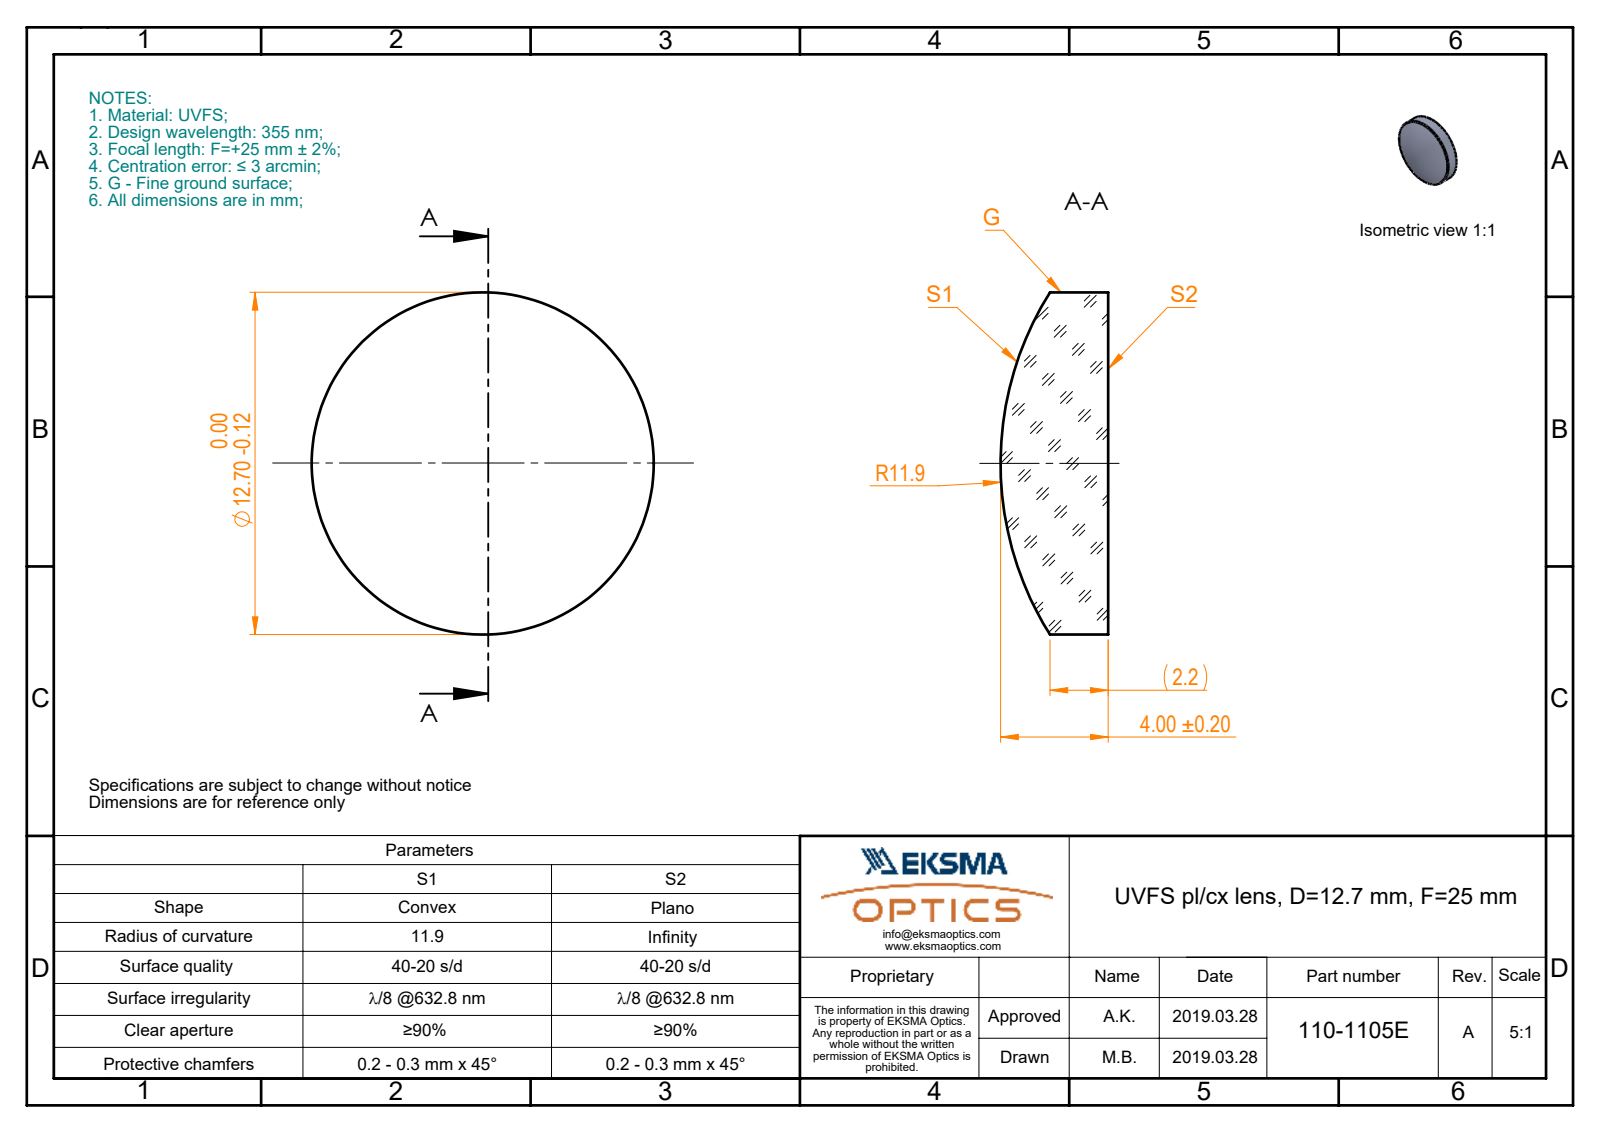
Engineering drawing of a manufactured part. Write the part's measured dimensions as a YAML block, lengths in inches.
part_name: "110-1105E UVFS pl-cx 12.7 F25"
step_written_by: "SolidWorks 2017 (CONFIG_CONTROL_DESIGN)"
units: inches
bodies: {solids: 1, faces: 5, planar: 1, cylindrical: 2, other: 2}
overall_size: [0.5, 0.5, 0.157]
volume: 0.024
surface_area: 0.543
round_bosses_or_shafts:
  - {diameter: 0.5, count: 1}
